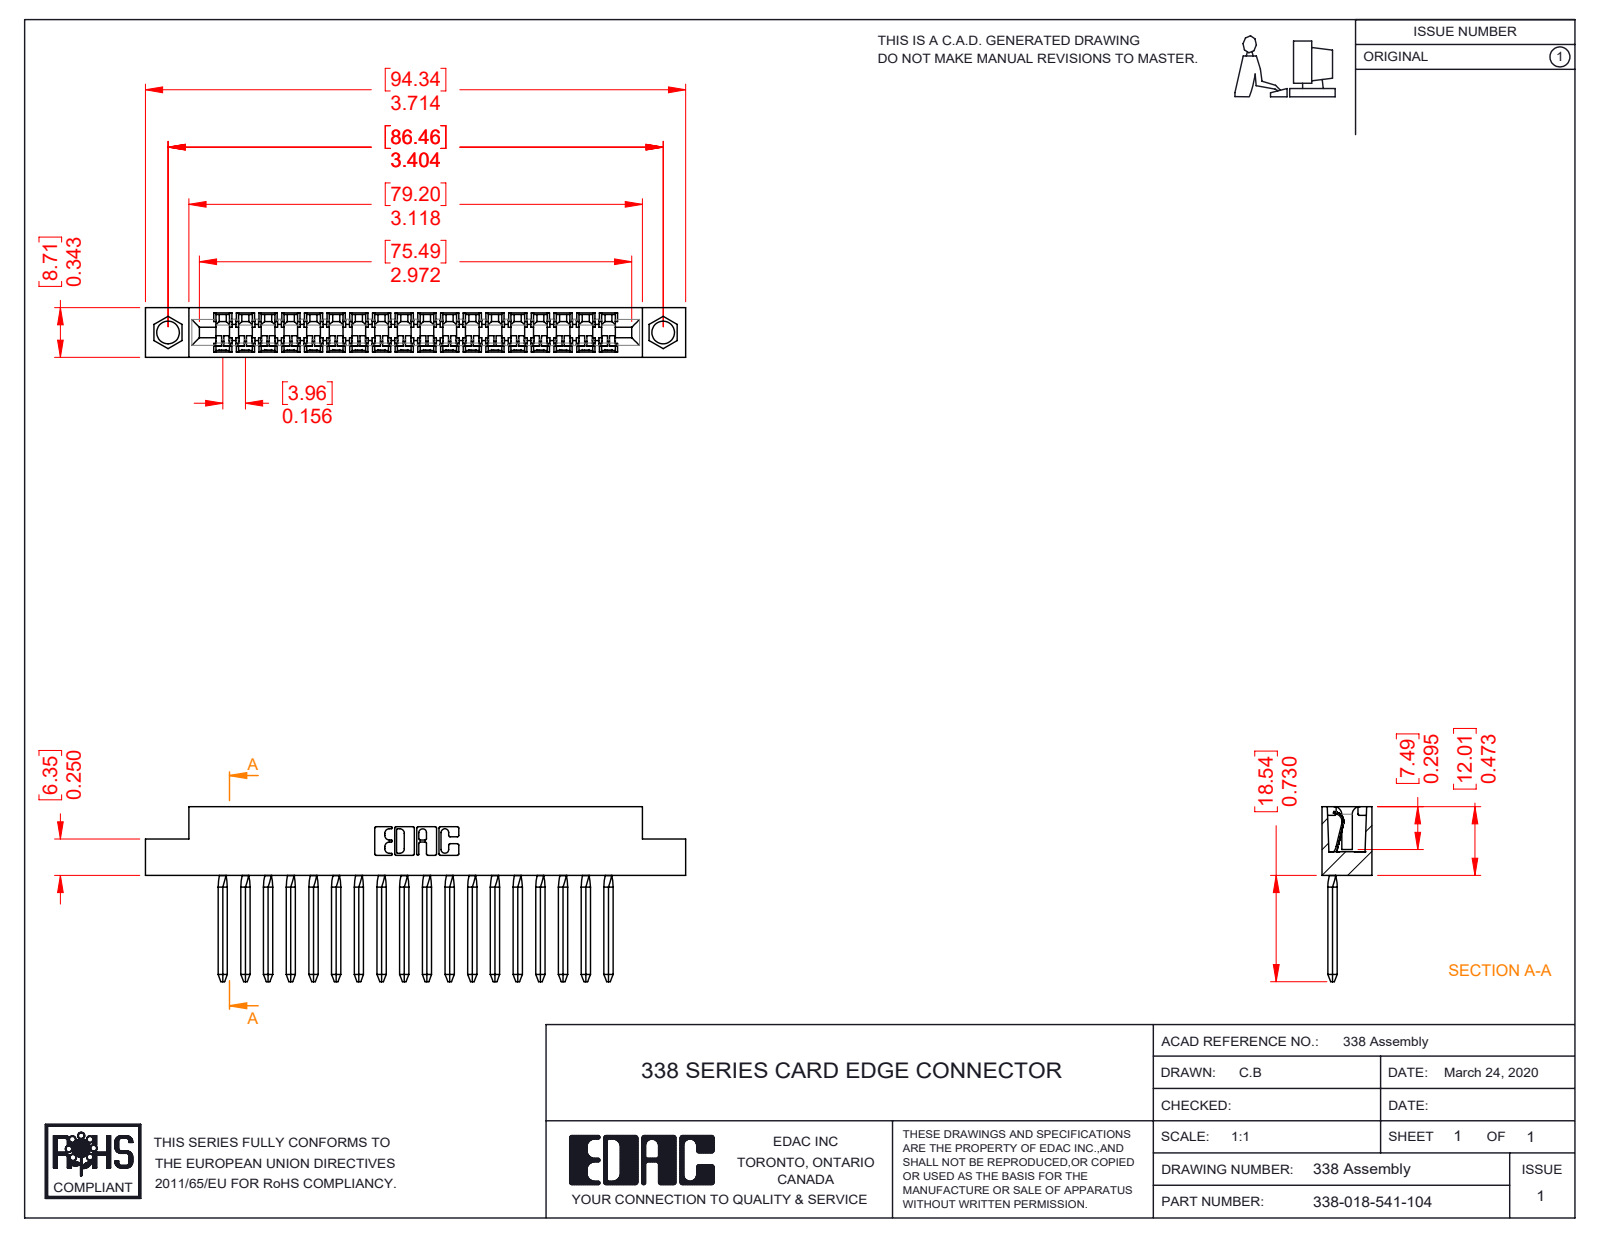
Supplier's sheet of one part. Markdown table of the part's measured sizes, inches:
| quantity | value |
| --- | --- |
| part name | 338-210-001_338-210-018-004; 338-290-001_541; 338-018-541-104 |
| STEP written by | SolidWorks 2016 (CONFIG_CONTROL_DESIGN) |
| units | inches |
| bodies | 19 solids, 1782 faces (1234 planar, 476 cylindrical, 72 other) |
| overall size | 3.714 × 1.203 × 0.343 |
| volume | 0.396 in³ |
| surface area | 15.71 in² |
| round holes (diameter × count) | 0.156 × 2 |
| partial cylindrical surfaces (radius × count) | 0.025 × 74, 0.01 × 22, 0.008 × 18, 0.055 × 15, 0.067 × 15, 0.1 × 14, 0.007 × 6, 0.031 × 6 |
| main face-to-face distances | 0.343, 0.156, 0.624, 0.11, 0.78, 0.468, 0.207, 0.135, 0.221, 0.312 |
| hole center spacings | 3.404 |
